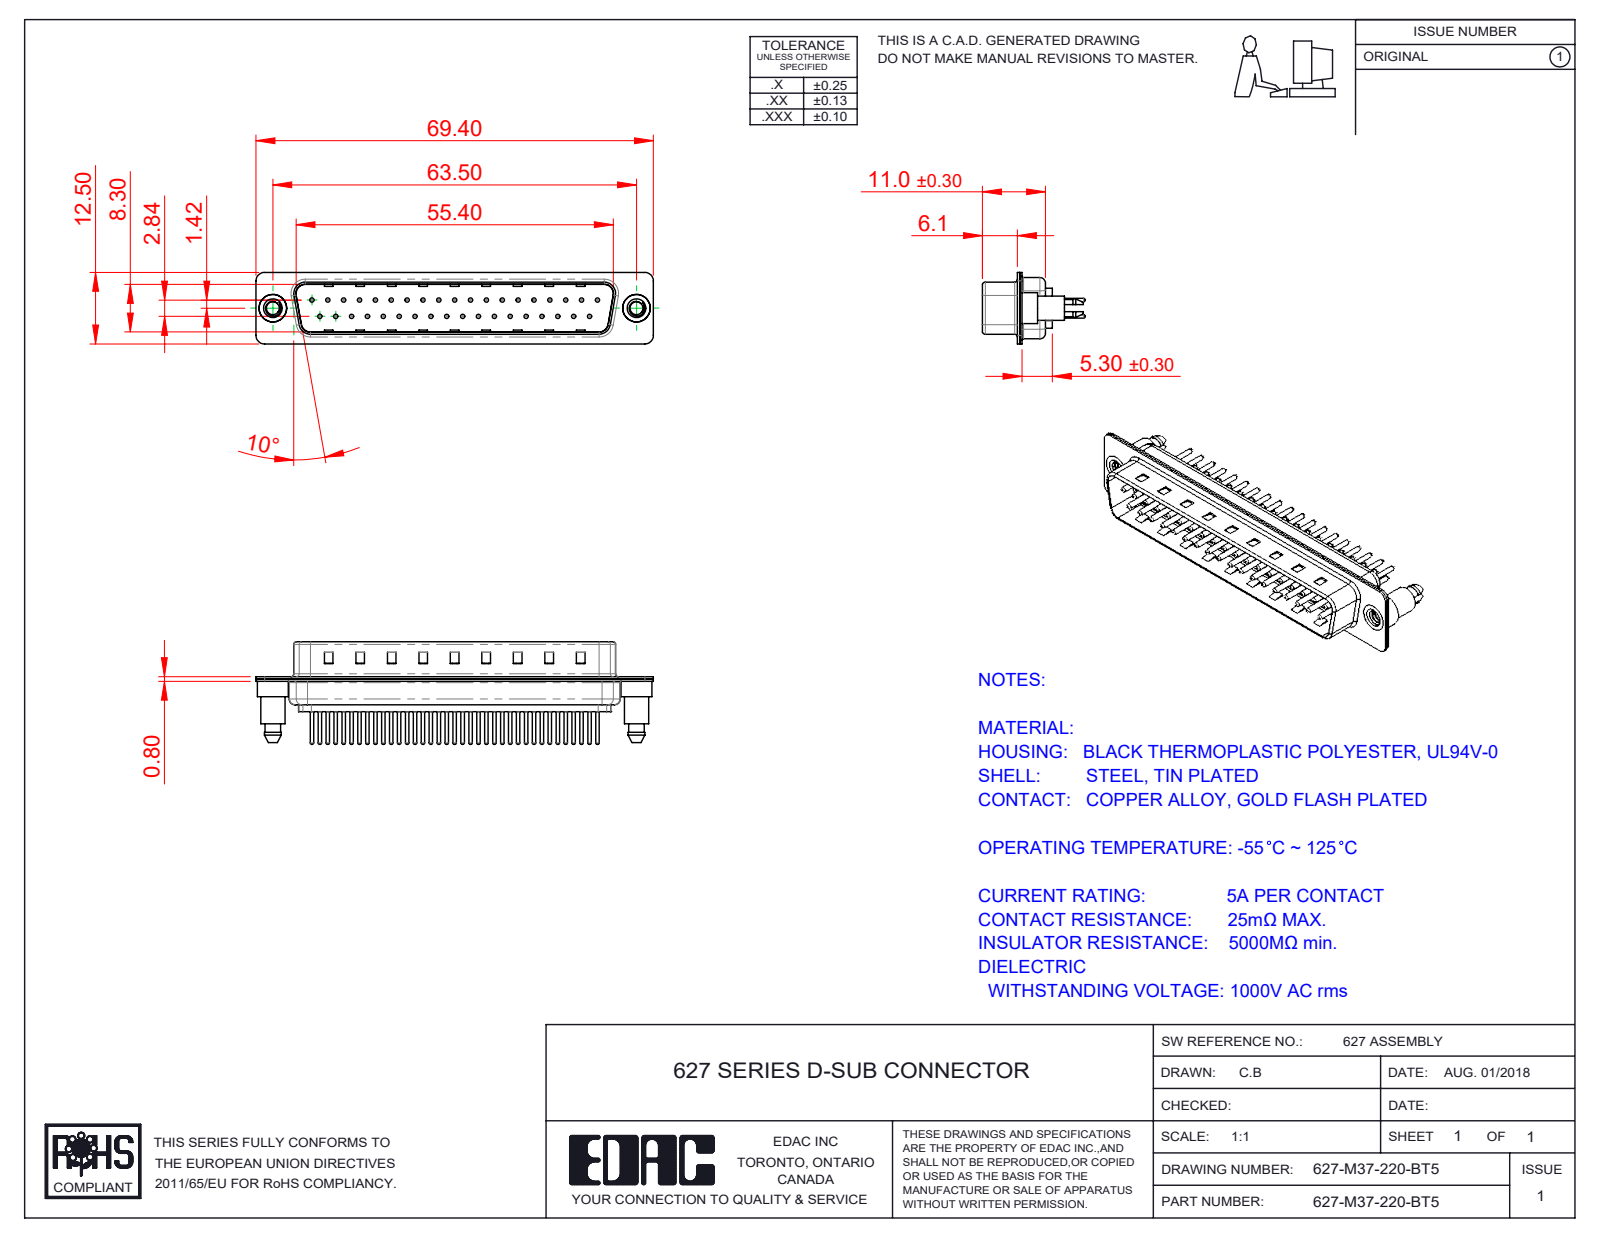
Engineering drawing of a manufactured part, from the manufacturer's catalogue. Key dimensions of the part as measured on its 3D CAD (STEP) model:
Part name (STEP PRODUCT): 627M Contact Row 2_20; 627-M37-220-BT5; 627M 4-40 Threaded Boardlock; 627M Housing_37 Contacts (+3 more)
STEP written by: SolidWorks 2020 (CONFIG_CONTROL_DESIGN)
Units: millimetres
Bodies: 42 solids, 1831 faces (478 planar, 691 cylindrical, 662 other)
Overall size (bounding box): 69.4 × 17.9 × 12.5
Volume: 3 902 mm³ · Surface area: 9 603 mm²
Round holes (diameter × count): ⌀0.75 ×37, ⌀1.6 ×37, ⌀2 ×37, ⌀2.26 ×2, ⌀4 ×2, ⌀4.8 ×2
Round bosses / shafts (diameter × count): ⌀1.5 ×37, ⌀0.6 ×37, ⌀5.4 ×2, ⌀4.9 ×2, ⌀4.25 ×2
Partial cylindrical surfaces — rounded edges, fillets, slot ends (radius × count): R1.5 ×18, R2 ×12, R1.6 ×10, R0.5 ×8, R0.25 ×4, R0.6 ×4, R0.65 ×4, R0.9 ×4
Main face-to-face distances: 0.4, 0.8, 9.5, 9.1, 8.7, 9.9, 1.2, 5.7, 0.75, 0.35
Hole centre spacings: 2.77, 5.54, 3.16, 8.31, 11.08, 13.85, 16.62, 19.39
